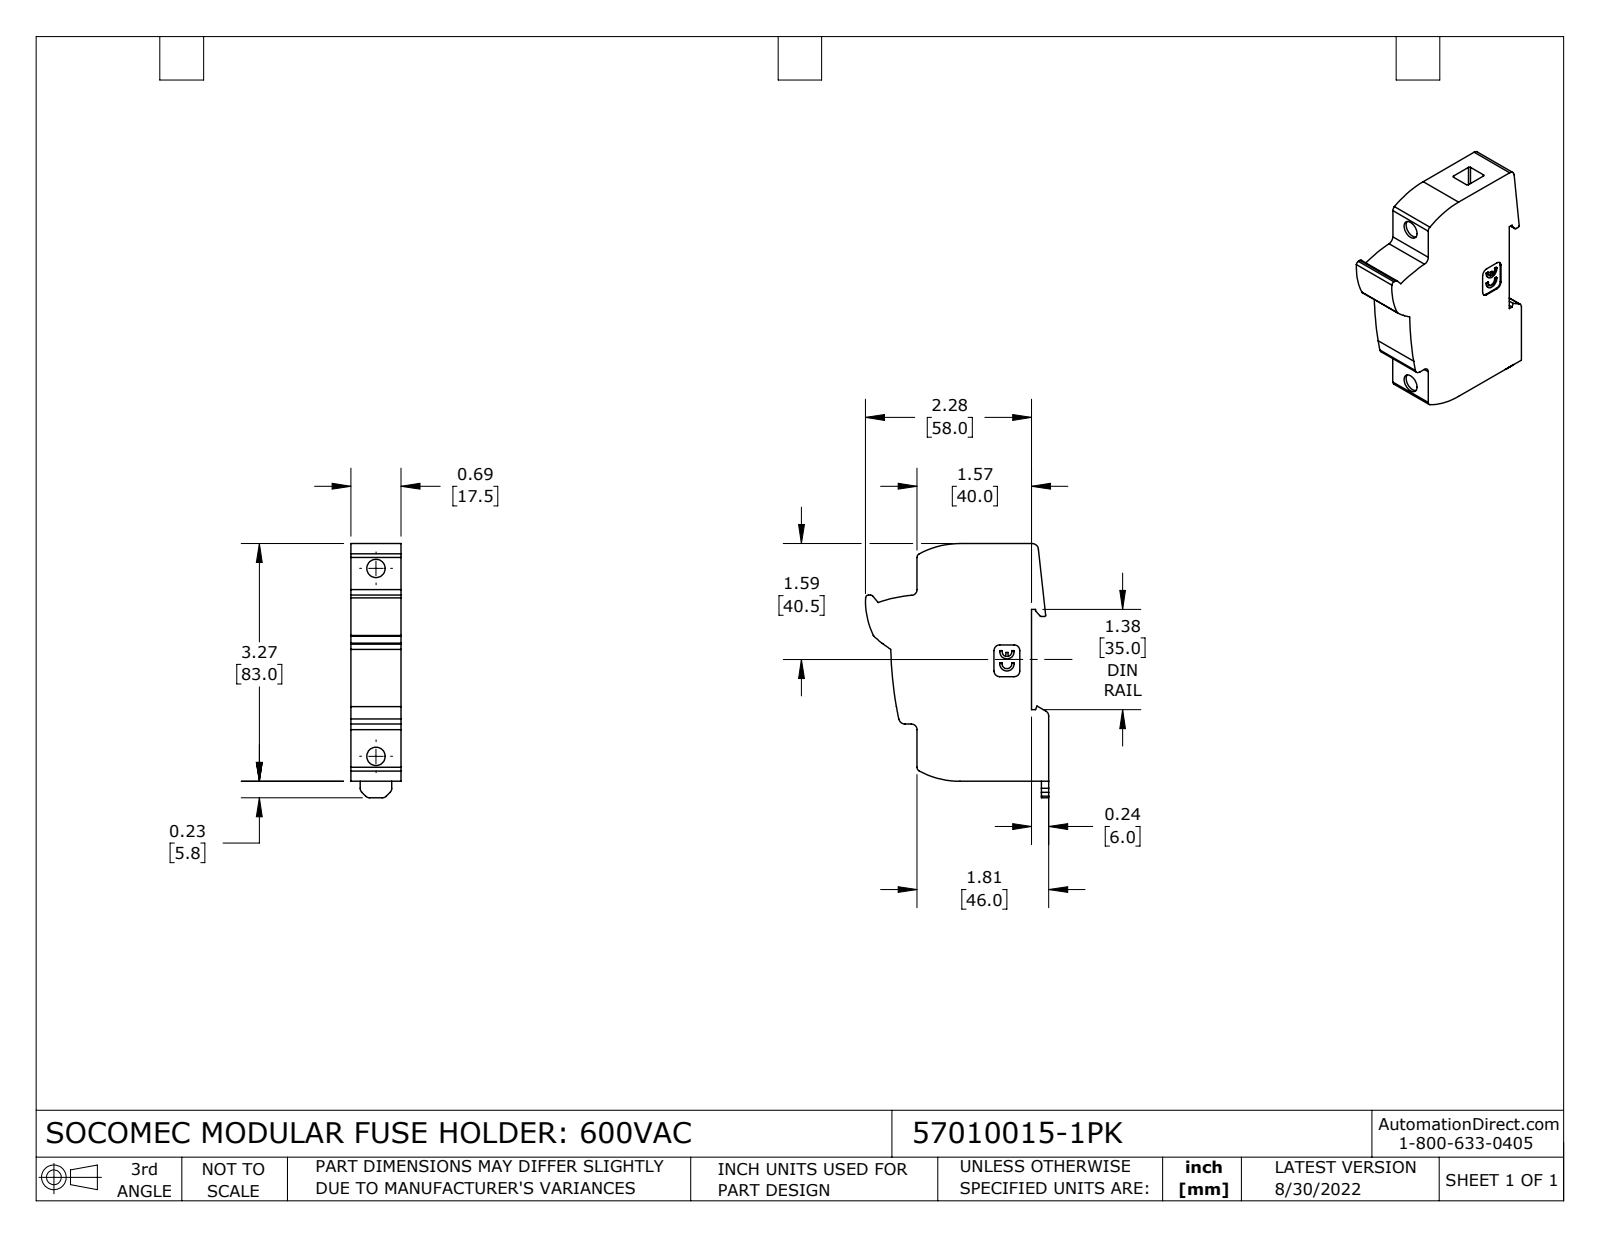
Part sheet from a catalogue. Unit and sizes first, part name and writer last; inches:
Units: inches
Overall size (bounding box): 3.496 × 2.52 × 0.689
Round holes (diameter × count): ⌀0.252 ×2
Partial cylindrical surfaces — rounded edges, fillets, slot ends (radius × count): R0.079 ×11, R0.02 ×5, R0.039 ×4, R0.059 ×2, R0.067 ×2, R0.087 ×2, R0.098 ×2, R1.186 ×2
Main face-to-face distances: 0.689, 0.236, 1.575, 3.268, 1.811, 0.199, 0.49, 0.291, 0.518, 0.281
Hole centre spacings: 2.583
Volume: 4.229 in³ · Surface area: 21.33 in²
Bodies: 1 solid, 105 faces (52 planar, 53 cylindrical, 0 other)
Part name (STEP PRODUCT): 57010015-1PK
STEP written by: SolidWorks 2021 (CONFIG_CONTROL_DESIGN)
